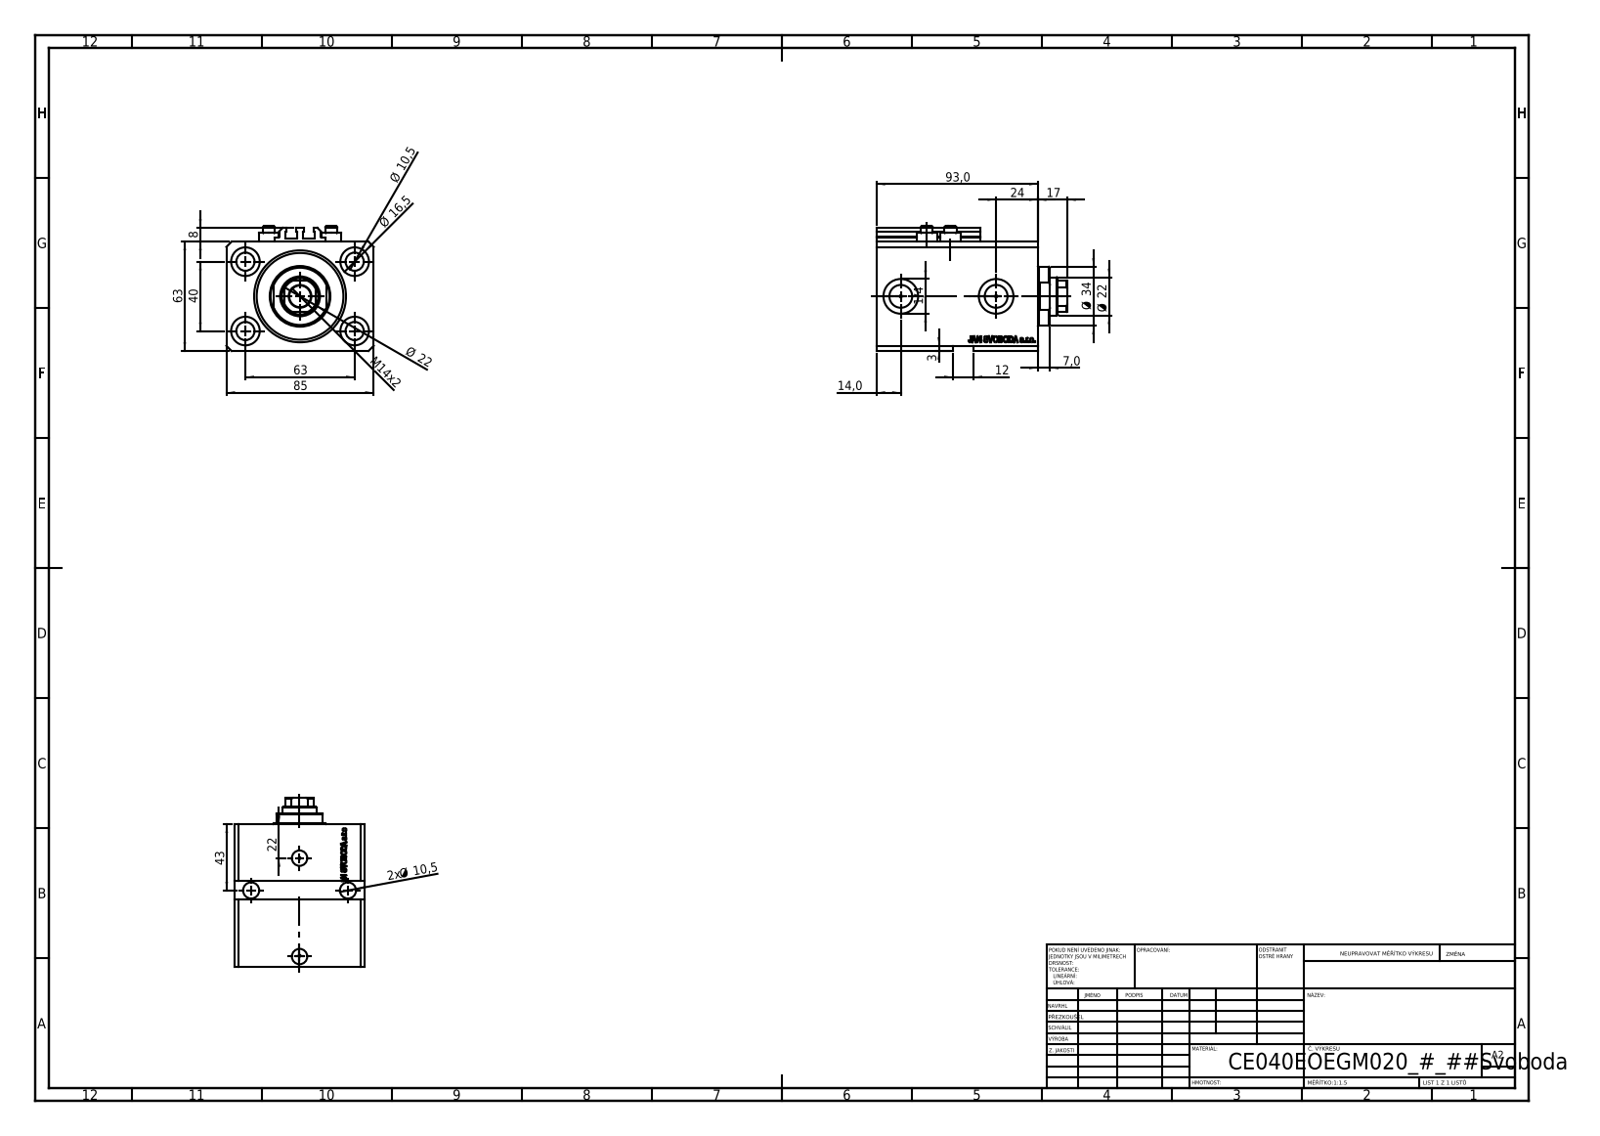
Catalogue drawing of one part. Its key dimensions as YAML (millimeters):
part_name: "V250CE_C_VCP; V250CE_E_Body; V250CE_VC_E; ALLEN BOLT V250CE"
step_written_by: "SolidWorks 2019 (CONFIG_CONTROL_DESIGN)"
units: millimeters
bodies: {solids: 8, faces: 1087, planar: 535, cylindrical: 126, other: 426}
overall_size: [110, 85, 72]
volume: 437253
surface_area: 95786
round_holes:
  - {diameter: 10.5, count: 6}
  - {diameter: 1.25, count: 4}
  - {diameter: 4, count: 4}
  - {diameter: 16.5, count: 4}
  - {diameter: 10, count: 2}
  - {diameter: 13.16, count: 2}
  - {diameter: 20, count: 2}
  - {diameter: 12.5, count: 1}
  - {diameter: 22, count: 1}
  - {diameter: 40, count: 1}
  - {diameter: 53, count: 1}
round_bosses_or_shafts:
  - {diameter: 11.6, count: 4}
  - {diameter: 7, count: 4}
  - {diameter: 34, count: 1}
partial_cylinders:
  - {radius: 0.2, count: 10}
  - {radius: 10.5, count: 1}
face_to_face_distances: [63, 85, 93, 17, 76, 11.4, 64.6, 81.6, 3, 65]
hole_center_spacings: [37.31, 63, 13.6, 15.4, 24.96, 28.02, 28.43, 33.62]
